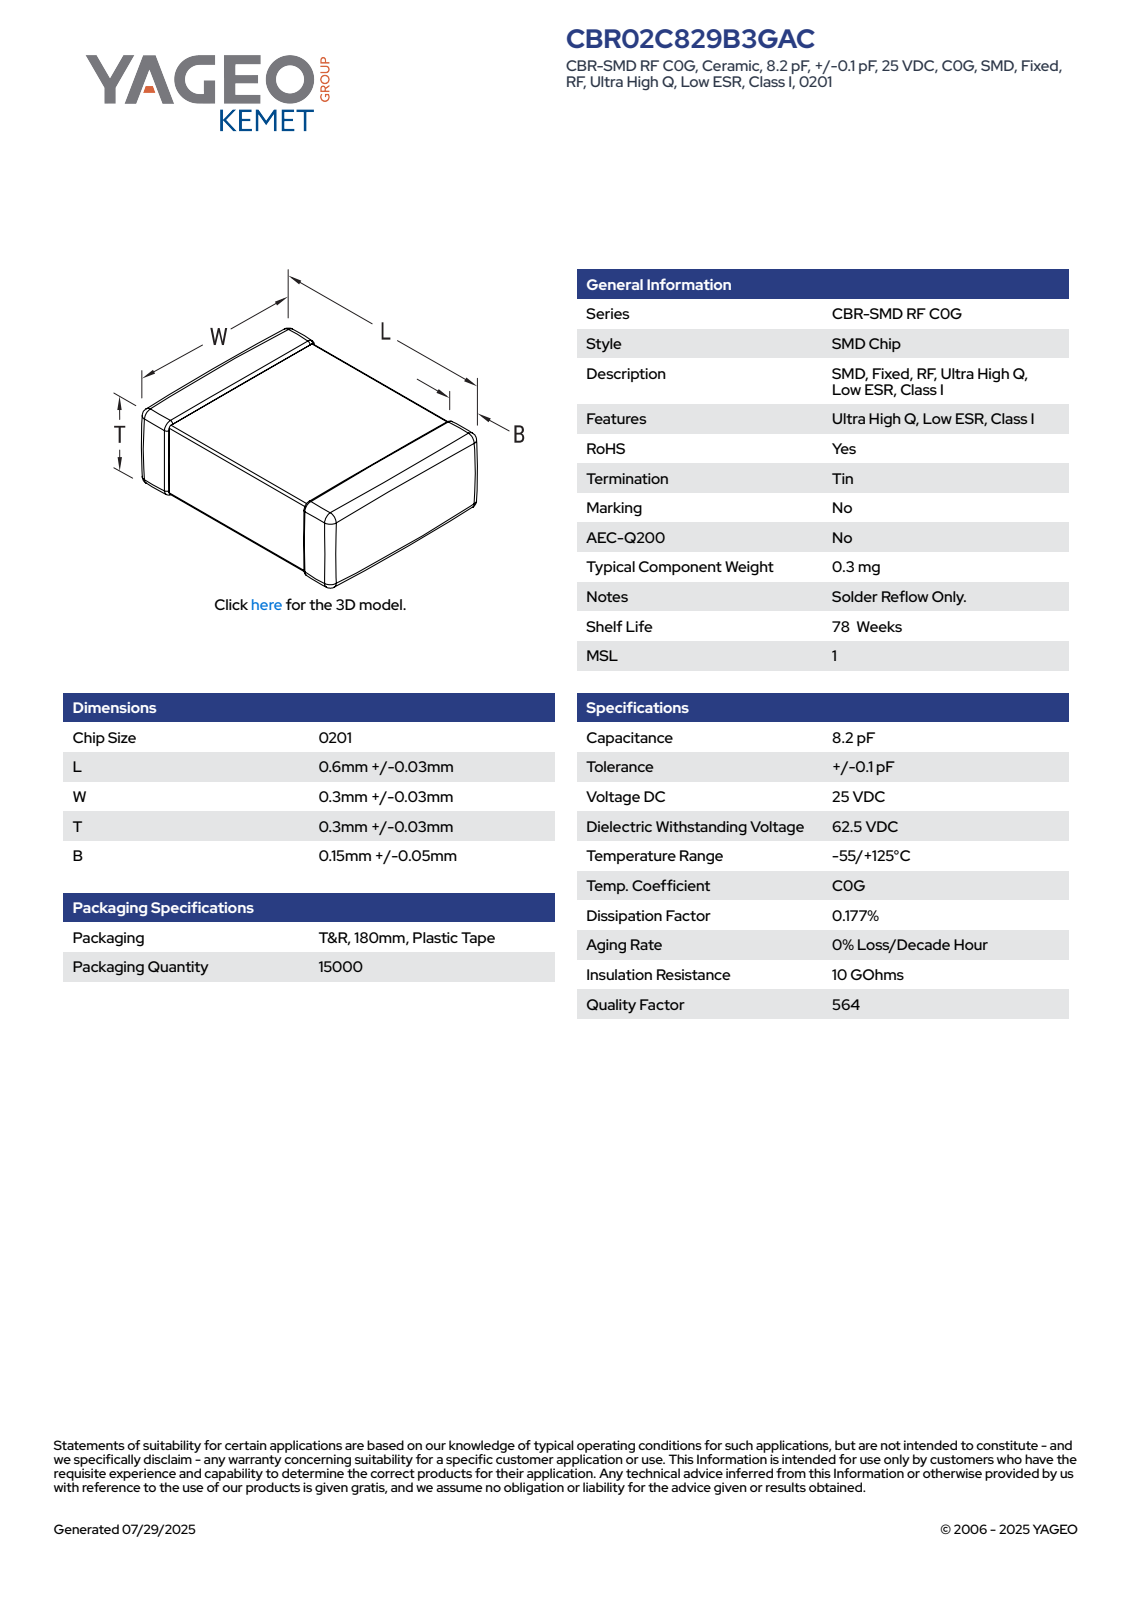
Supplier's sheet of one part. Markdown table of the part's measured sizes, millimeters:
| quantity | value |
| --- | --- |
| part name | CCS_CCSTDNOS_0201_L0.63W0.33T0.33B0.2 |
| STEP written by | SolidWorks 2014 (AUTOMOTIVE_DESIGN) |
| units | millimeters |
| bodies | 4 solids, 121 faces (71 planar, 34 cylindrical, 16 other) |
| overall size | 0.63 × 0.33 × 0.33 |
| volume | 0.067 mm³ |
| surface area | 1 mm² |
| main face-to-face distances | 0.32, 0.33, 0.31, 0.63 |
